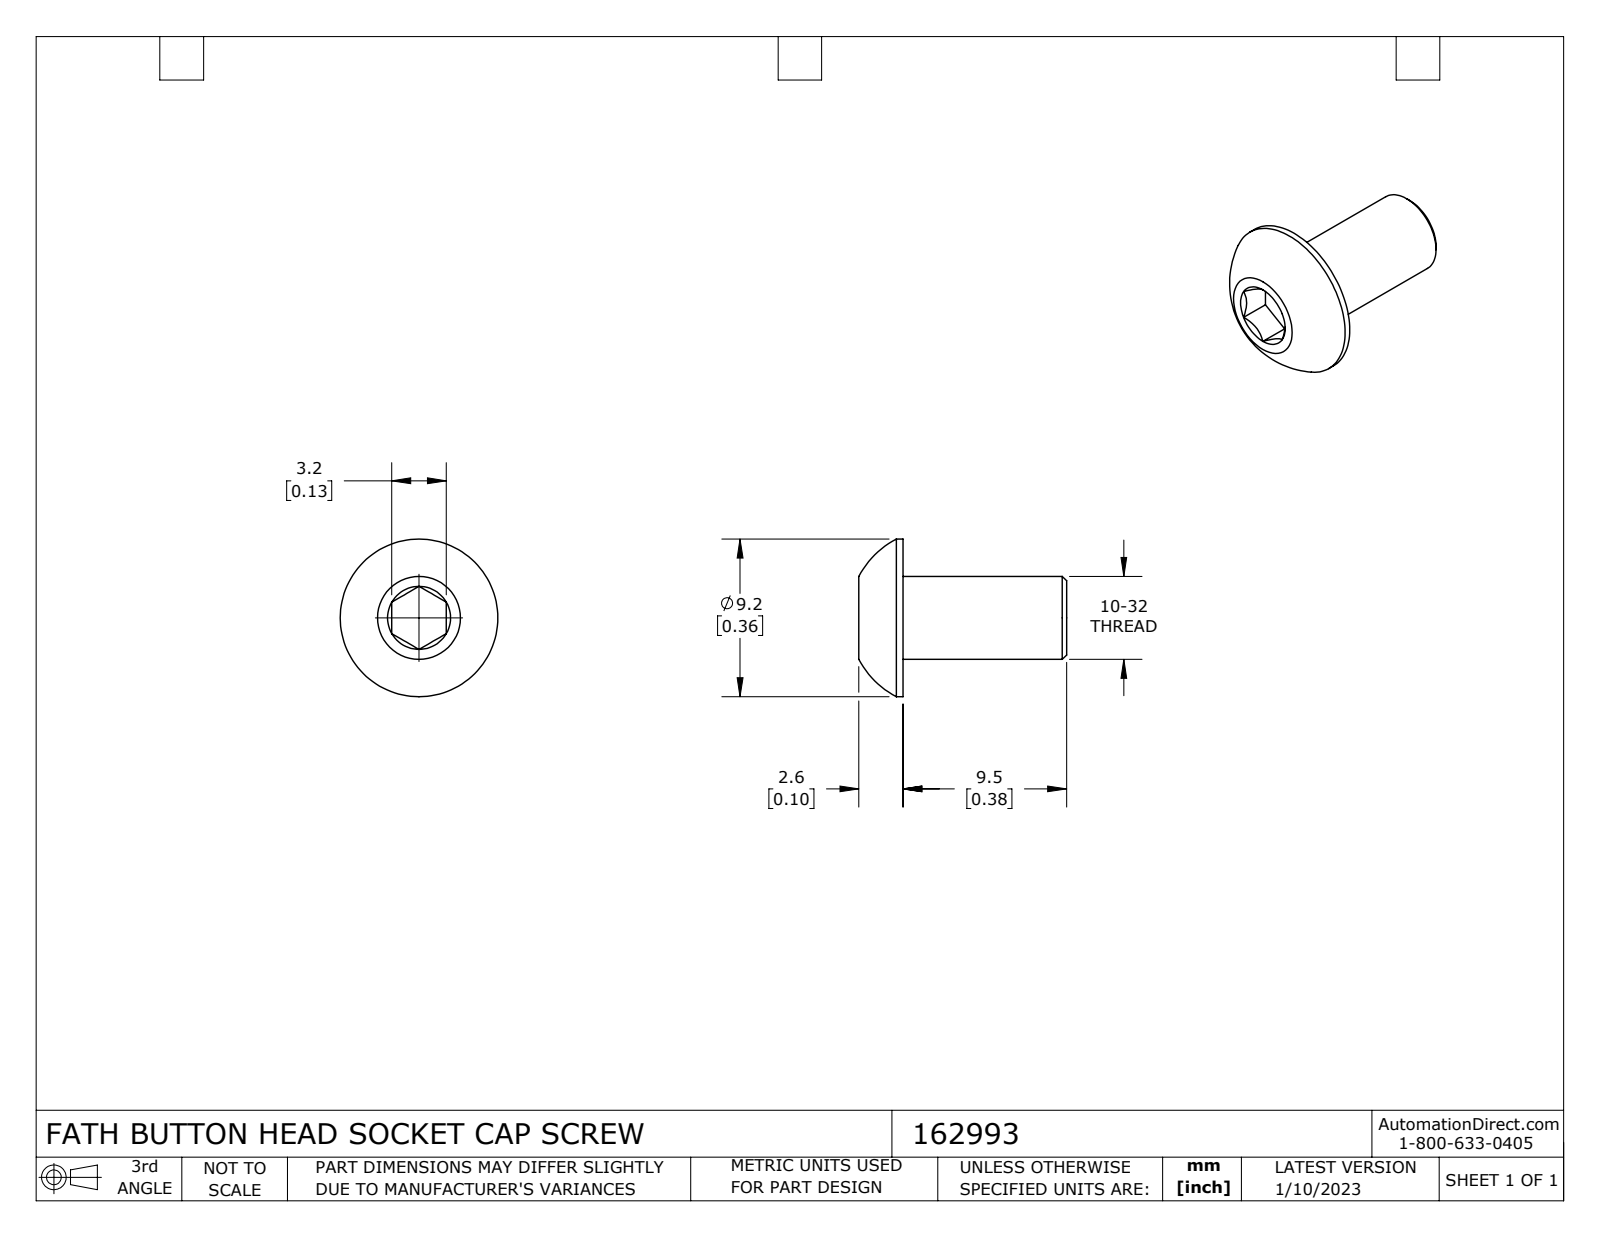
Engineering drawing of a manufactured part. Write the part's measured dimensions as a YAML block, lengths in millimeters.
part_name: "162993"
step_written_by: "SolidWorks 2021 (CONFIG_CONTROL_DESIGN)"
units: millimeters
bodies: {solids: 1, faces: 28, planar: 12, cylindrical: 4, other: 12}
overall_size: [12.1, 9.2, 9.2]
volume: 280
surface_area: 327
round_bosses_or_shafts:
  - {diameter: 9.2, count: 1}
  - {diameter: 4.8, count: 1}
face_to_face_distances: [9.5, 3.2, 10.3, 0.8, 12.1, 2.6, 1.8, 1.6]
